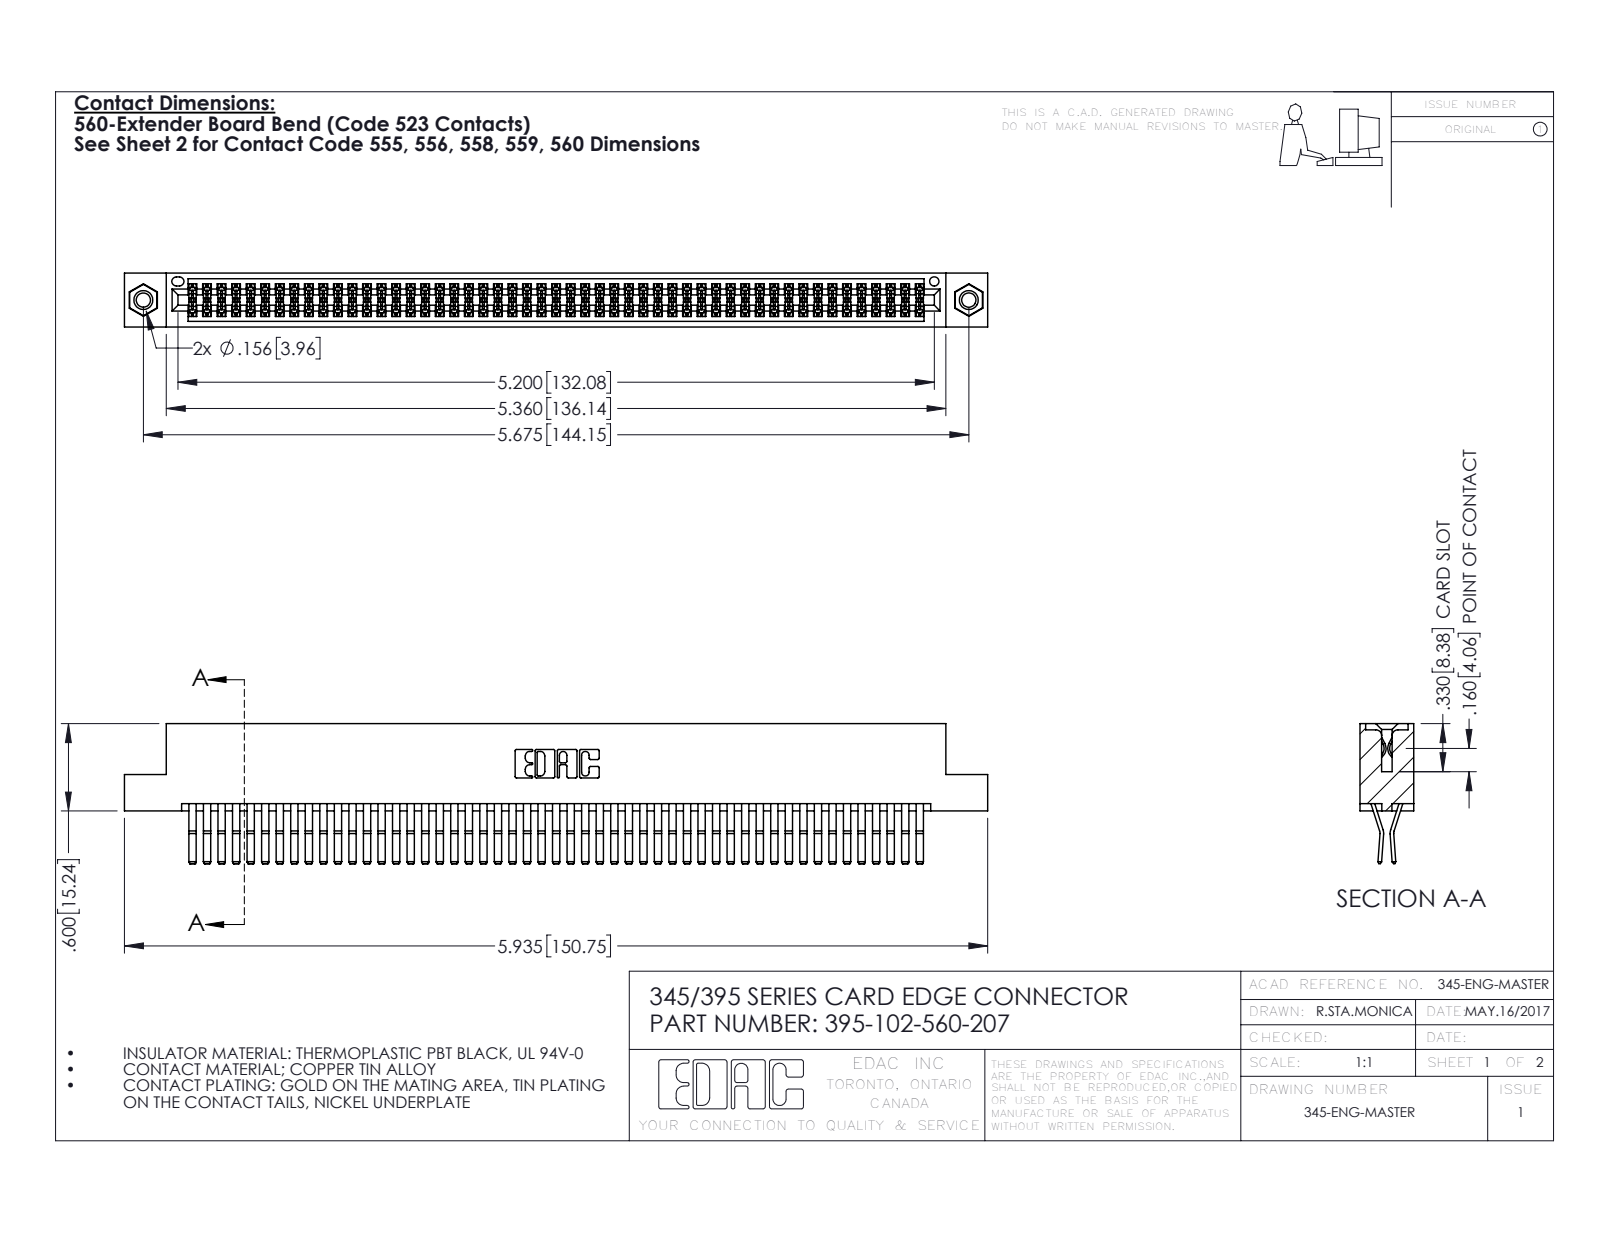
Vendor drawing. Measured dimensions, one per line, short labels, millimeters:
name: 345-250-001_345-250-005-103; 345 Part_Flush Mounting Lugs - 0.156 Dia-TI; 395-102-560-207; 345-292-001_560 Tail
written by: SolidWorks 2016 (CONFIG_CONTROL_DESIGN)
unit: mm
bodies: 105 solids, 5490 faces (3478 planar, 1996 cylindrical, 16 other)
size: 150.7 × 24.4 × 9.4
volume: 15 400 mm³; area: 24 660 mm²
holes: 2× ⌀2.5, 2× ⌀3.2, 2× ⌀4, 1× ⌀1.6
bosses: 2× ⌀3.9
rounds: 154× R0.2, 22× R0.3, 6× R0.2, 6× R0.8, 3× R0.7, 2× R0.3, 2× R0.4, 2× R0.5
face distances: 0.6, 1.8, 7.6, 9.4, 5.1, 2.5, 6.9, 5.7, 4.4, 3.8
hole spacings: 6.9, 138.2, 144.1
